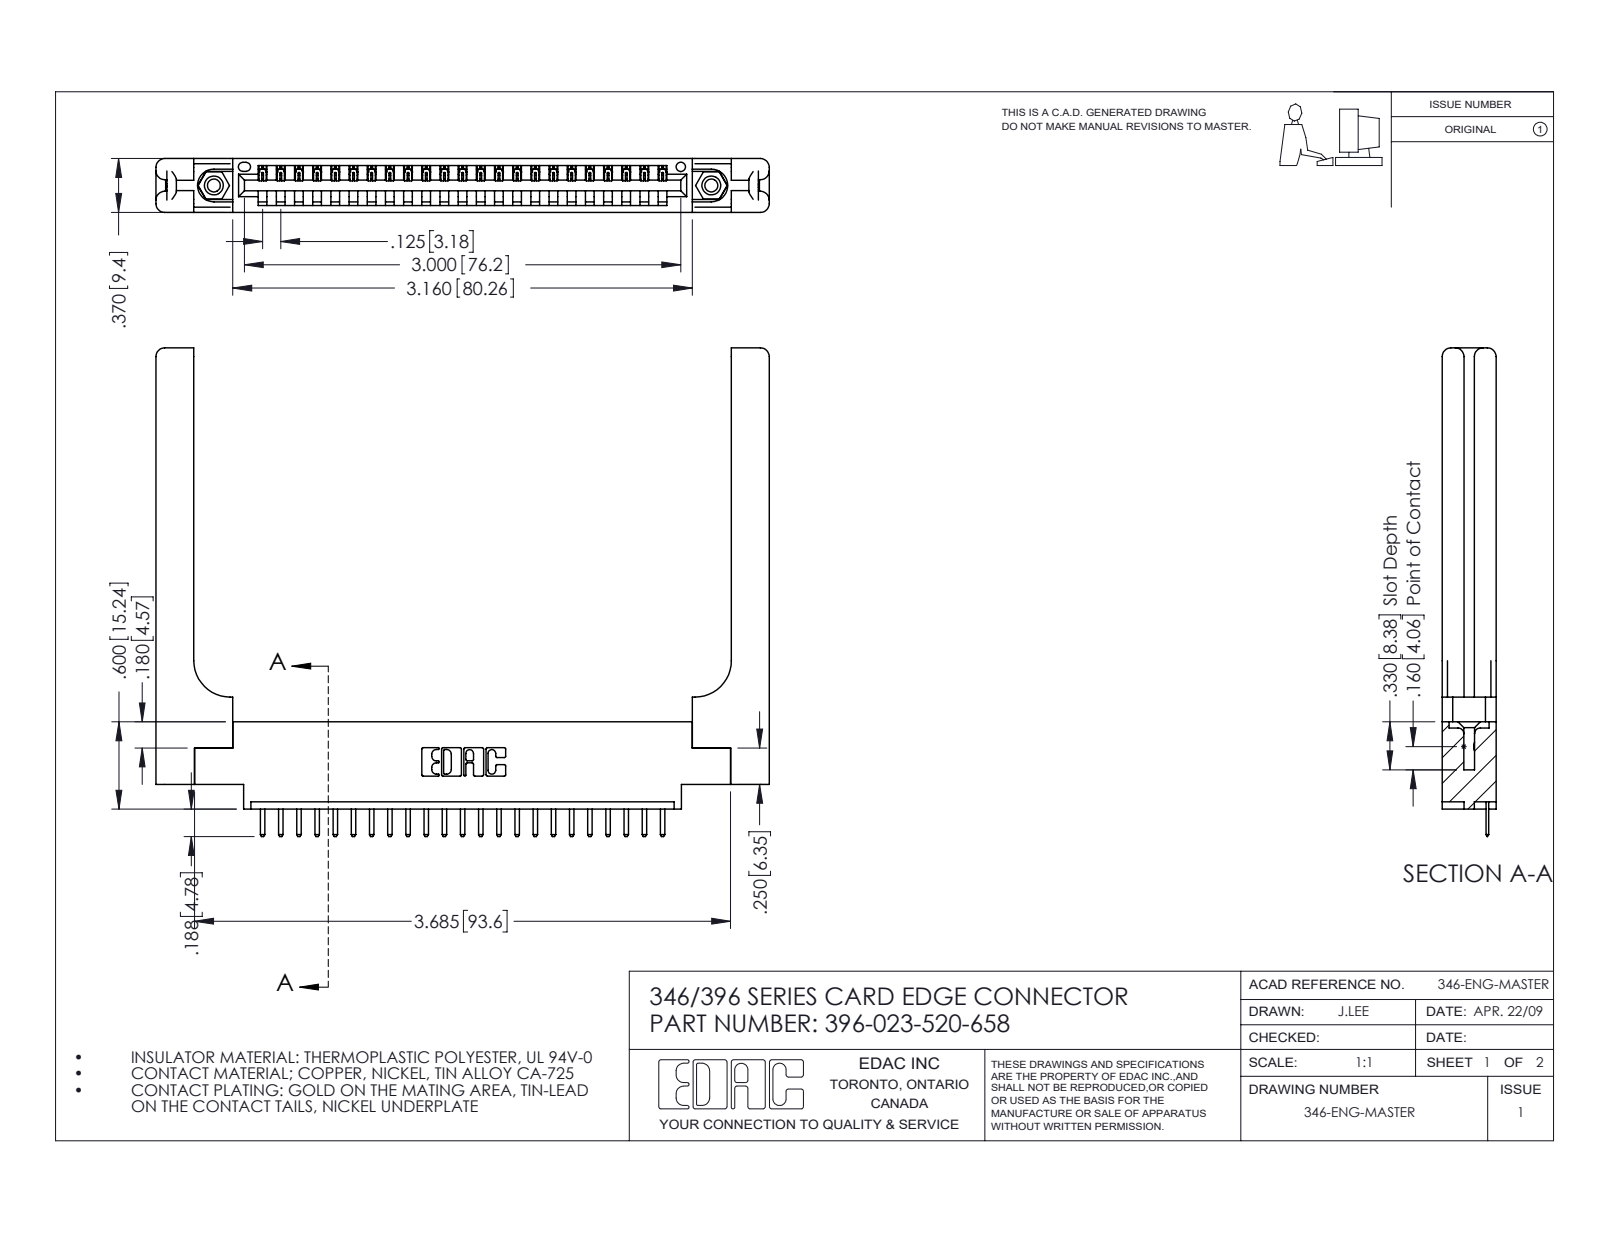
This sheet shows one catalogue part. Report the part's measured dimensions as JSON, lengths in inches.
{"part_name": "346 Part_0.170 Offset - 0.156 Dia-TH; 346-220-058_345-220-058; 345-250-001_345-250-001-102; 345-292-001_345-293-120 (+1 more)", "step_written_by": "SolidWorks 2016 (CONFIG_CONTROL_DESIGN)", "units": "inches", "bodies": {"solids": 28, "faces": 1808, "planar": 1194, "cylindrical": 554, "other": 60}, "overall_size": [4.216, 3.358, 0.37], "volume_in3": 1.063, "surface_area_in2": 26.78, "round_holes": [[0.089, 2], [0.125, 2], [0.156, 2], [0.064, 1]], "round_bosses_or_shafts": [[0.155, 2]], "partial_cylinders_radius": [[0.01, 48], [0.006, 46], [0.01, 22], [0.06, 16], [0.007, 6], [0.031, 6], [0.026, 3], [0.03, 2]], "face_to_face_distances": [0.37, 0.072, 0.15, 0.148, 0.048, 0.322, 0.25, 0.102, 0.22, 0.173], "hole_center_spacings": [0.246, 3.212, 3.42]}
